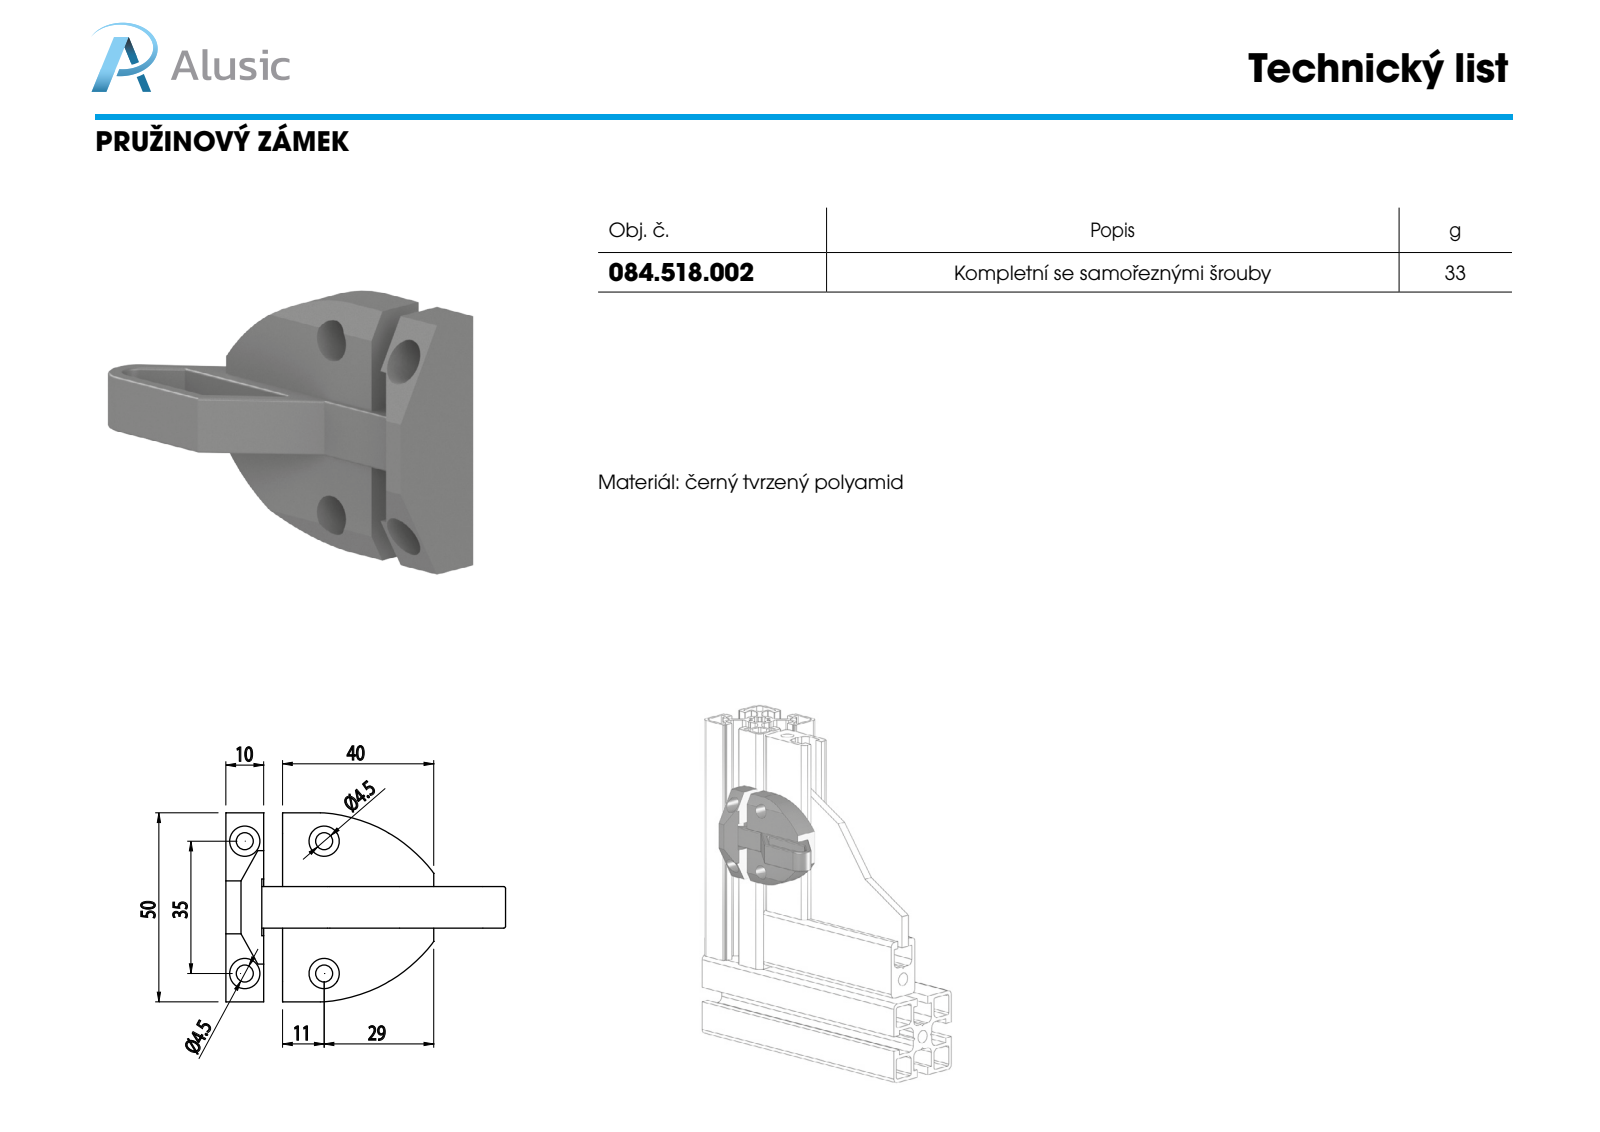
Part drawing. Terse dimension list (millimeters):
name: 084.518.002
written by: SolidWorks 2016 (CONFIG_CONTROL_DESIGN)
unit: mm
bodies: 3 solids, 101 faces (43 planar, 44 cylindrical, 14 other)
size: 74 × 50 × 30
volume: 29 936 mm³; area: 13 074 mm²
holes: 4× ⌀4.5, 4× ⌀8
rounds: 23× R0.5, 2× R40, 1× R3, 1× R6
face distances: 13, 15, 3, 10, 11, 14, 2, 5, 16, 19.5
hole spacings: 21, 35, 40.82
